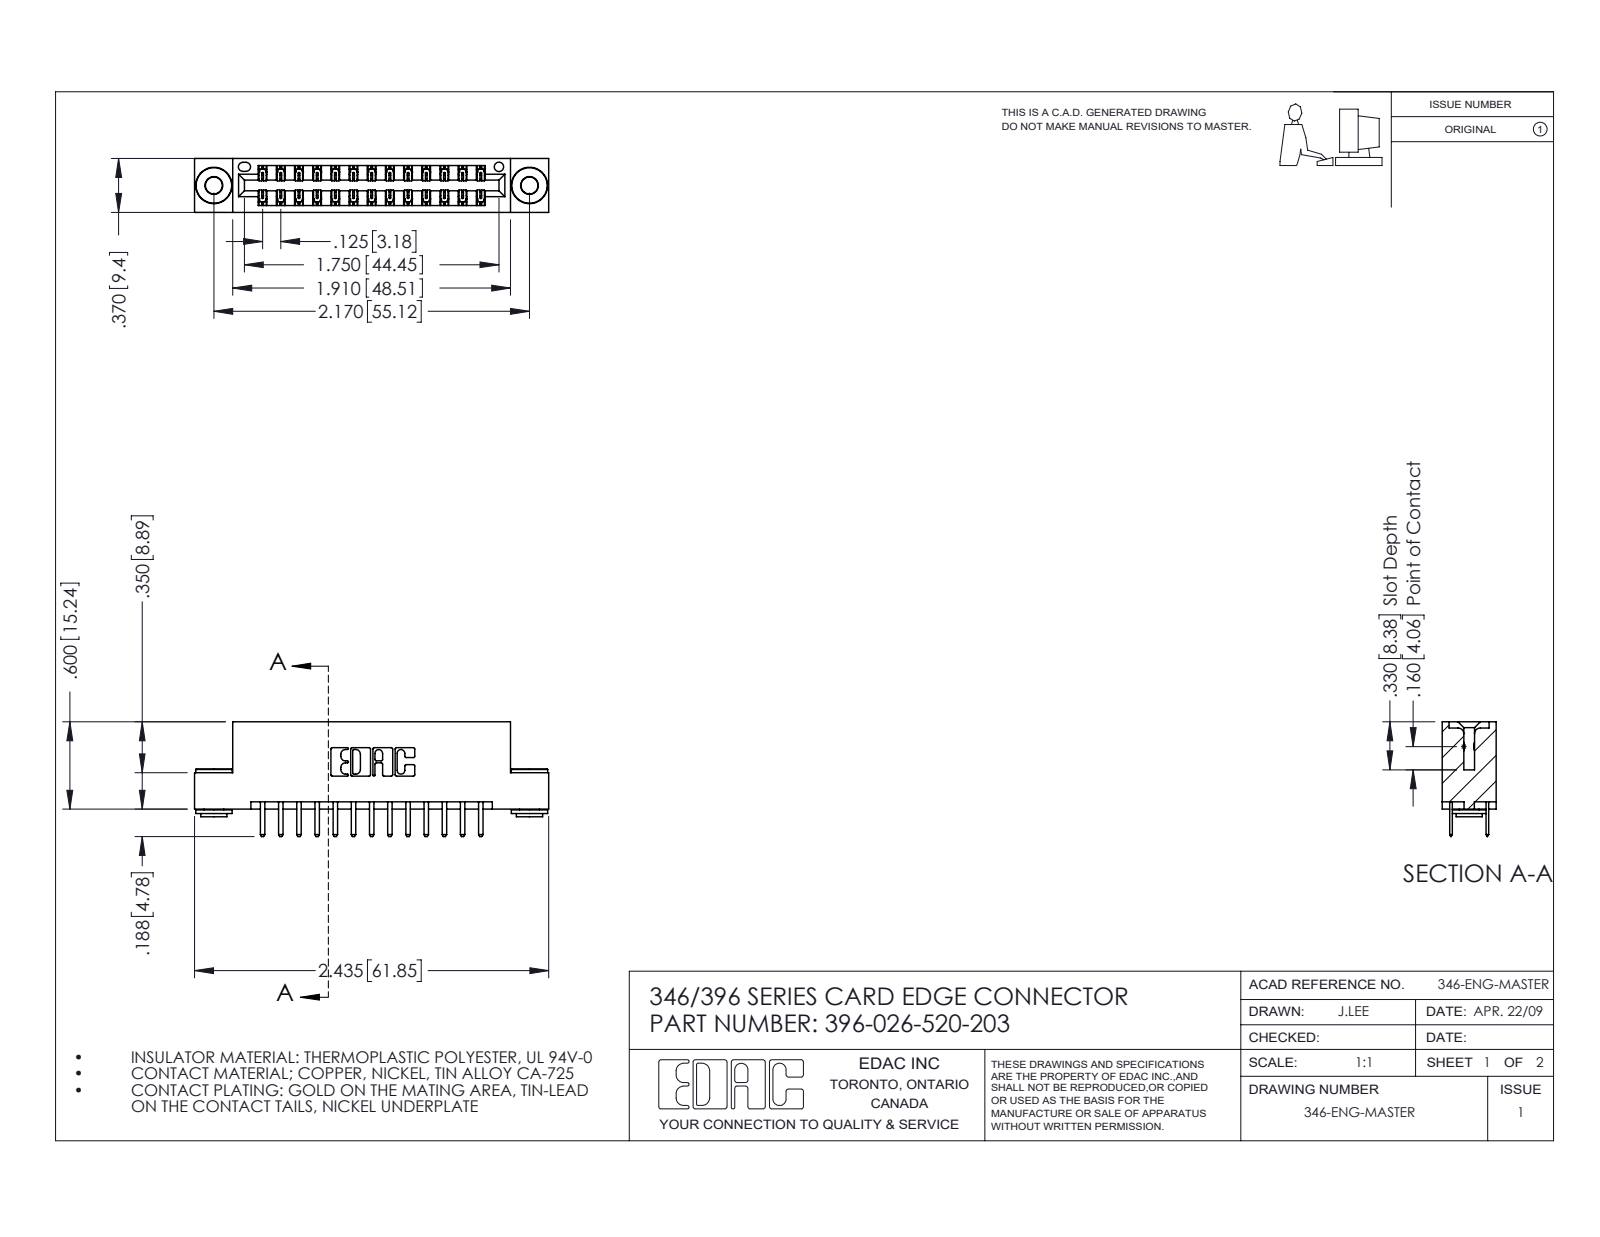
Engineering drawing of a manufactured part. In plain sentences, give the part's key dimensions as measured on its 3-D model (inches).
The part is named "345-250-002_345-250-002-102; 346 Part_Flush Mounting Lugs - 0.156 Dia-TH; 396-026-520-203; 345-292-001_345-293-120". Its 3-D file was written by "SolidWorks 2016 (CONFIG_CONTROL_DESIGN)". It is 29 solids with 1616 faces: 1048 planar, 560 cylindrical and 8 other. Overall it measures 2.435 by 0.788 by 0.37 inches. Its volume is 0.355 cubic inches and its surface area 11.97 square inches. Round holes: 2 of diameter 0.116, 2 of diameter 0.156, 1 of diameter 0.064. Round bosses or shafts: 2 of diameter 0.25, 2 of diameter 0.18, 2 of diameter 0.136. Partial cylindrical surfaces (rounded edges, fillets, slot ends): 39 of radius 0.006, 30 of radius 0.01, 22 of radius 0.01, 6 of radius 0.007, 6 of radius 0.031, 3 of radius 0.026, 2 of radius 0.014, 2 of radius 0.022. The main face-to-face distances are 0.25, 0.048, 0.322, 0.37, 0.025, 0.275, 0.072, 0.298, 0.148, 0.222. The hole center spacings are 0.246, 1.964, 2.17.
